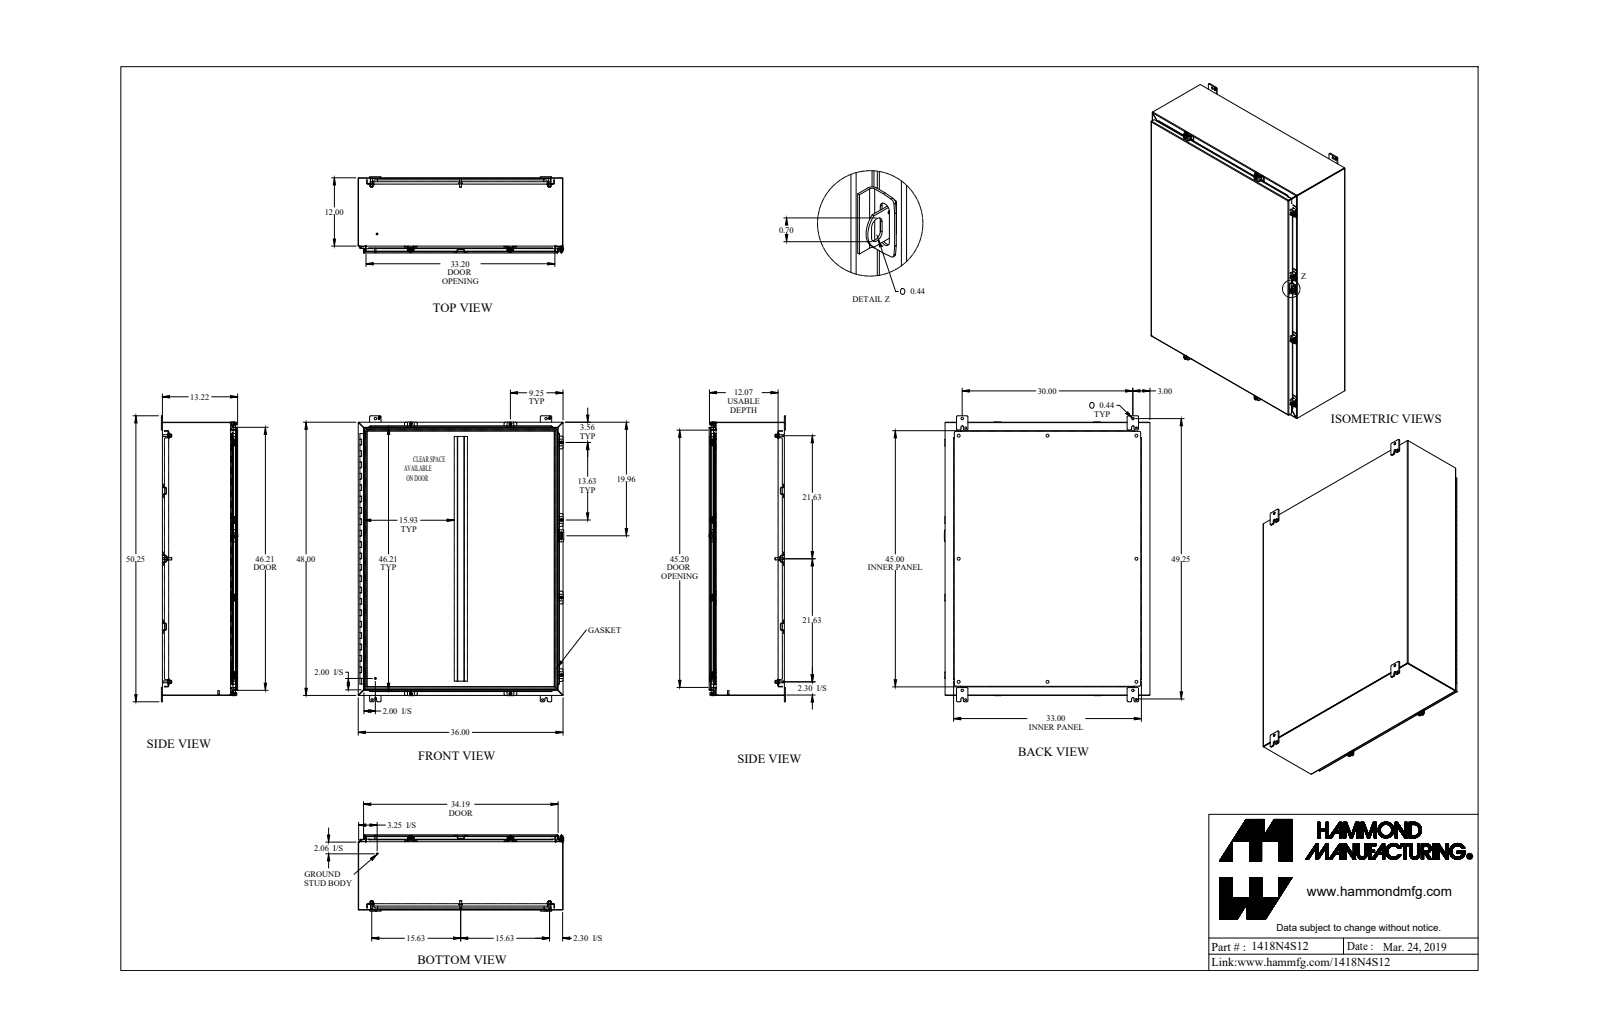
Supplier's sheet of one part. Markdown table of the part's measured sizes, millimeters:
| quantity | value |
| --- | --- |
| part name | 1418N4S12_Default |
| STEP written by | SolidWorks 2019 (CONFIG_CONTROL_DESIGN) |
| units | millimeters |
| bodies | 69 solids, 2398 faces (1397 planar, 869 cylindrical, 132 other) |
| overall size | 1276.4 × 917.6 × 341.3 |
| volume | 10 350 000 mm³ |
| surface area | 10 660 000 mm² |
| round holes (diameter × count) | 5.4 × 8, 6.7 × 8, 9.5 × 8, 12.7 × 8, 7.8 × 4, 8 × 4, 11.1 × 4, 11.3 × 4, 3.2 × 1, 4.7 × 1 |
| round bosses / shafts (diameter × count) | 16.5 × 8, 12.7 × 8, 9.9 × 8, 9.5 × 8, 8.4 × 8, 6.2 × 8, 25.4 × 4, 7.1 × 2 |
| partial cylindrical surfaces (radius × count) | 6.4 × 48, 4.8 × 42, 1.2 × 39, 3.6 × 39, 0.9 × 22, 2.7 × 22, 2.9 × 16, 3.6 × 16 |
| main face-to-face distances | 1.8, 333.8, 332, 335.7, 2.4, 23.8, 25.6, 307.6, 305.8, 26.2 |
| hole center spacings | 965.3, 182.8, 396.9, 621.5, 1098.6, 1168, 1308.3, 549.3 |
